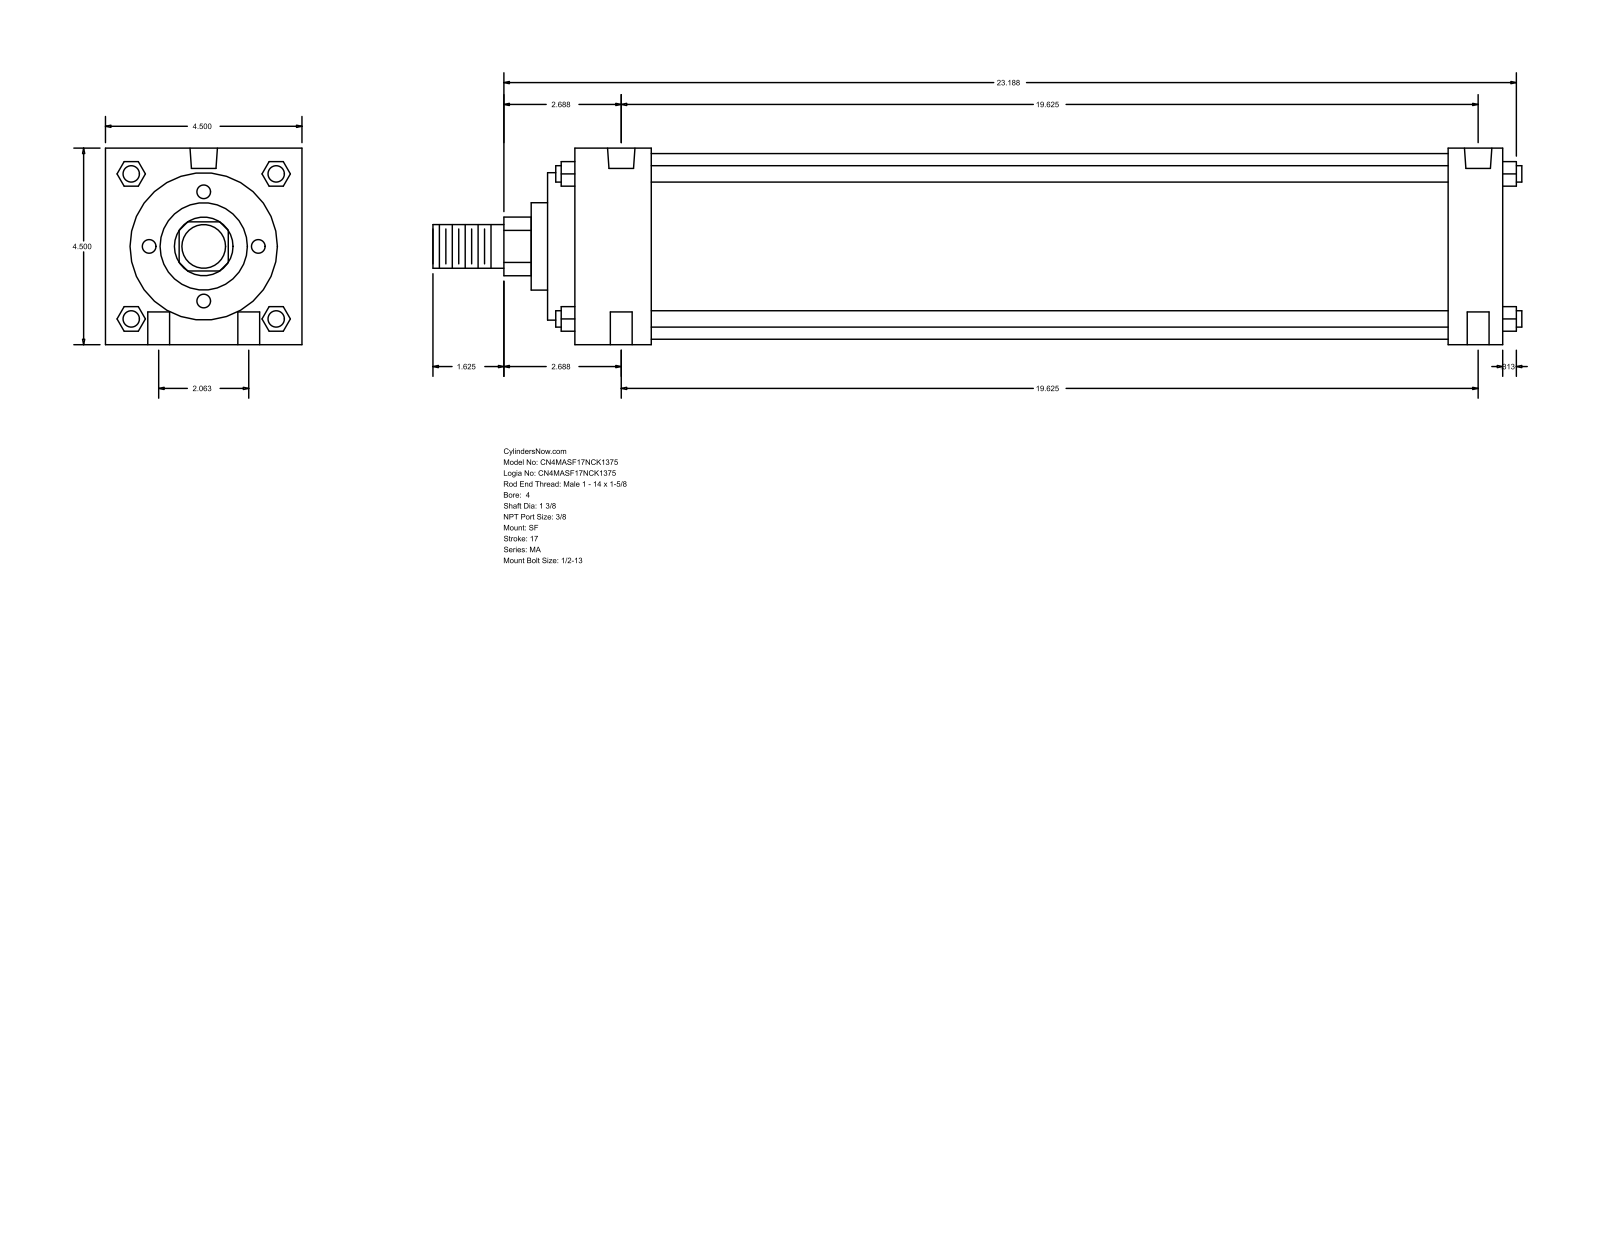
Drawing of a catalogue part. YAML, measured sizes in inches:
part_name: "MA_SF__0400_1.375"
step_written_by: "GSSL Pune (CONFIG_CONTROL_DESIGN)"
units: inches
bodies: {solids: 0, faces: 126, planar: 95, cylindrical: 31, other: 0}
overall_size: [24.937, 4.5, 4.5]
round_holes:
  - {diameter: 0.5, count: 4}
  - {diameter: 0.437, count: 2}
  - {diameter: 0.627, count: 2}
round_bosses_or_shafts:
  - {diameter: 0.375, count: 4}
  - {diameter: 4.25, count: 1}
  - {diameter: 3.375, count: 1}
  - {diameter: 2, count: 1}
  - {diameter: 1.375, count: 1}
  - {diameter: 1, count: 1}
partial_cylinders:
  - {radius: 0.672, count: 1}
face_to_face_distances: [4.5, 21.25, 21.875, 0.625, 20.625, 20, 1.25, 2.375, 1.75, 18.25]
hole_center_spacings: [1.031, 19.652, 19.625, 2.062, 19.733, 19.25]
